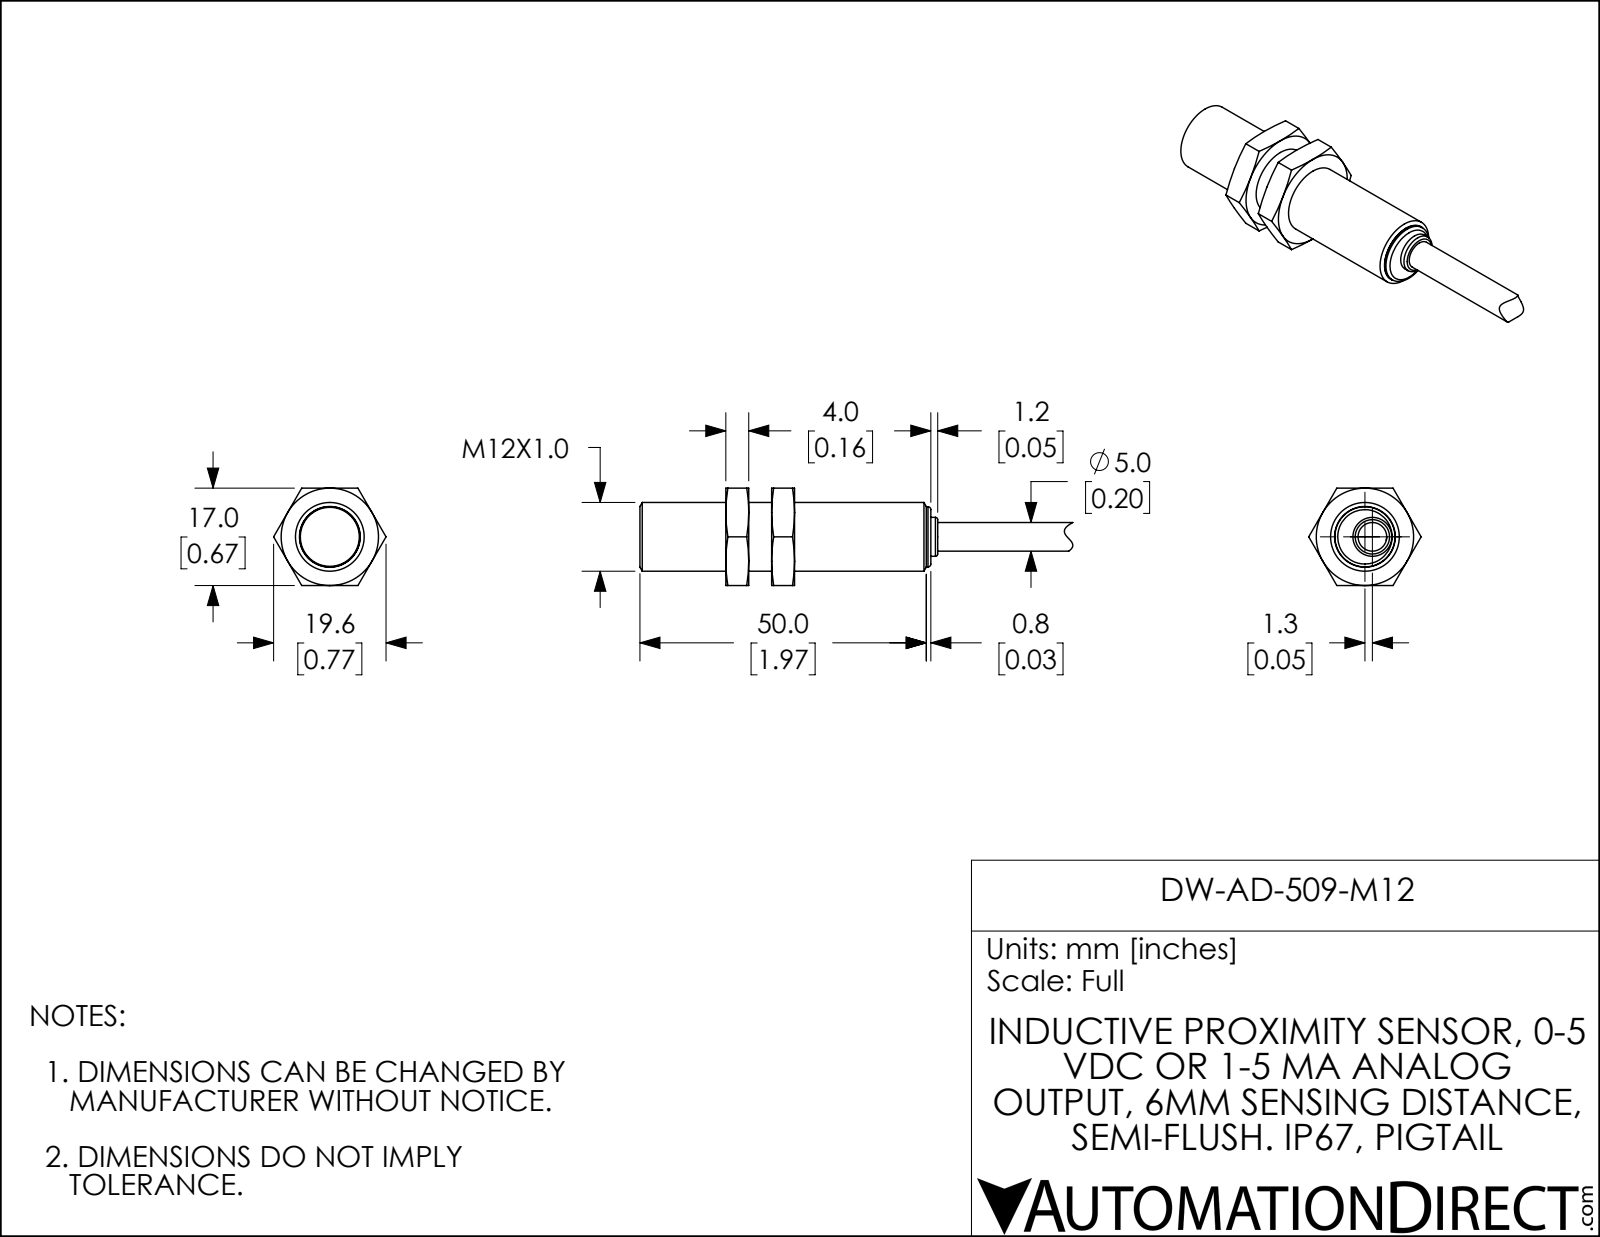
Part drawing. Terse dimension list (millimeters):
name: DW-AD-509-M12
written by: SolidWorks 2018 (AUTOMOTIVE_DESIGN)
unit: mm
bodies: 4 solids, 21 faces (9 planar, 6 cylindrical, 6 other)
size: 75.6 × 12 × 12
volume: 6 360 mm³; area: 2 990 mm²
holes: 1× ⌀5
bosses: 1× ⌀12, 1× ⌀10.5, 1× ⌀10.3, 1× ⌀6.8
face distances: 50, 49.8, 1.3, 1.1, 48.7, 50.8, 50.6, 49.5, 0.8, 47
